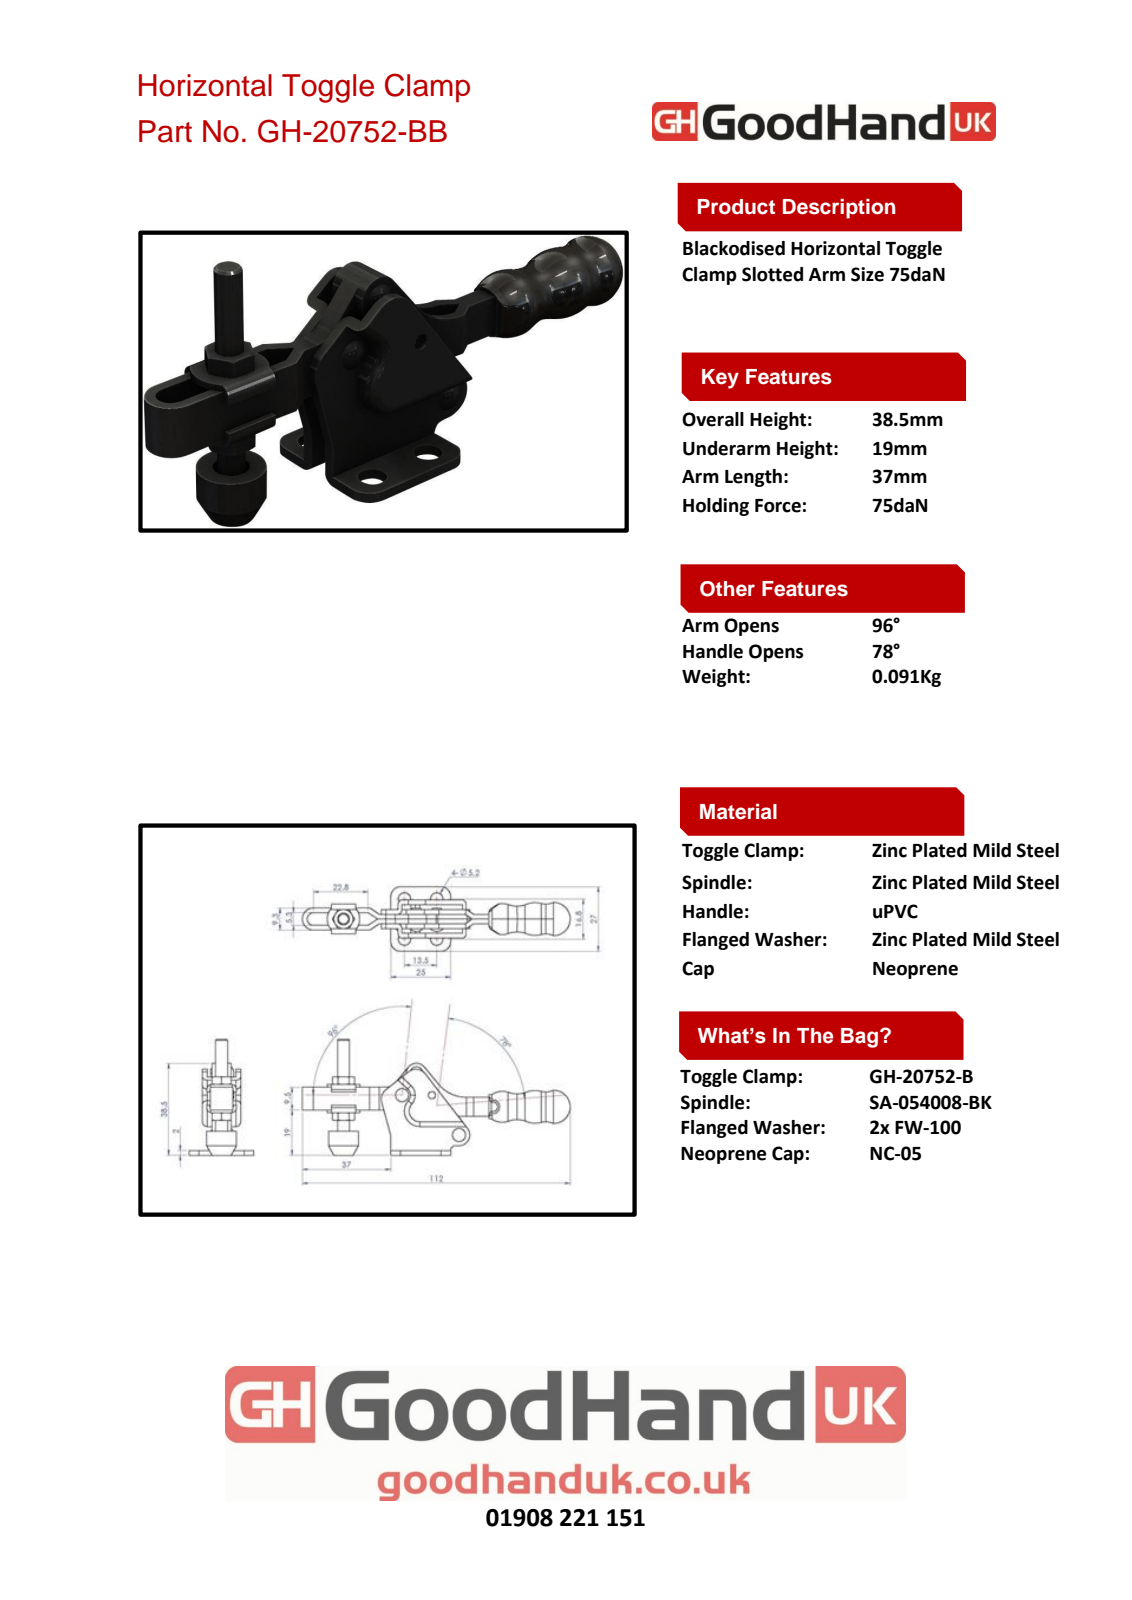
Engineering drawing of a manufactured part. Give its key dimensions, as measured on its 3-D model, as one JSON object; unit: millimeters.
{"part_name": "120752B05; 120752B08; 120752B01; 820752B82 (+7 more)", "step_written_by": "SolidWorks 2016 (AUTOMOTIVE_DESIGN)", "units": "millimeters", "bodies": {"solids": 17, "faces": 431, "planar": 152, "cylindrical": 171, "other": 108}, "overall_size": [112, 48.58, 27], "volume_mm3": 13579, "surface_area_mm2": 18218, "round_holes": [[3.03, 7], [2, 4], [5.2, 4], [3.05, 2], [4.2, 1], [5, 1], [6.5, 1], [9, 1]], "round_bosses_or_shafts": [[3, 4], [12.5, 1]], "partial_cylinders_radius": [[2, 13], [1, 7], [4, 5], [2.2, 4], [5, 4], [4.5, 3], [2.65, 1], [3.5, 1]], "face_to_face_distances": [2, 4, 6, 8, 10, 12, 3.35, 1.35, 0.65, 2.65], "hole_center_spacings": [4.76, 11.19, 13.5, 16.8, 20.13, 21.55, 26.86, 39.9]}
